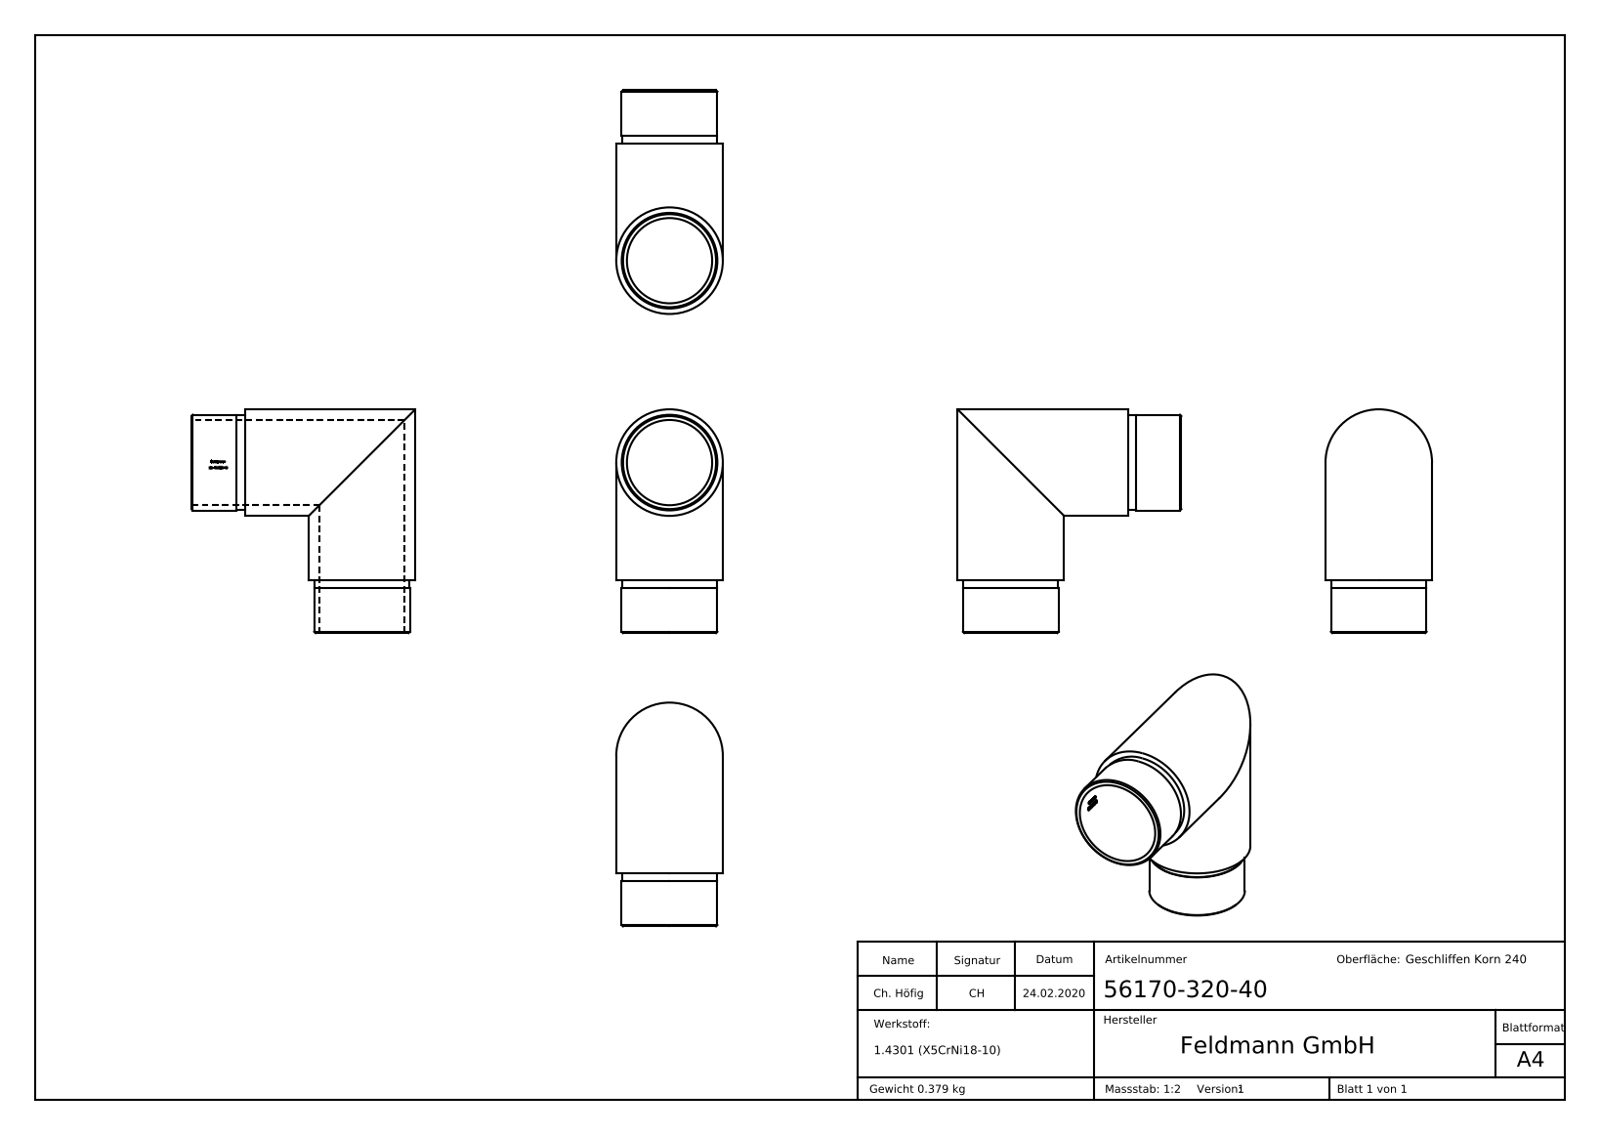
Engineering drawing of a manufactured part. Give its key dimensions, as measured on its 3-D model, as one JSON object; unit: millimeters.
{"part_name": "56170-320-40", "step_written_by": "SolidWorks 2015 (CONFIG_CONTROL_DESIGN)", "units": "millimeters", "bodies": {"solids": 1, "faces": 261, "planar": 111, "cylindrical": 36, "other": 114}, "overall_size": [84, 84, 40], "volume_mm3": 47967, "surface_area_mm2": 29364, "round_holes": [[32, 2]], "round_bosses_or_shafts": [[40, 2], [35.9, 2], [35.5, 2]], "partial_cylinders_radius": [[16.1, 1]], "face_to_face_distances": [20, 17, 3, 0.53, 0.83, 2.45, 0.56, 2.61, 1.78, 1.21]}
